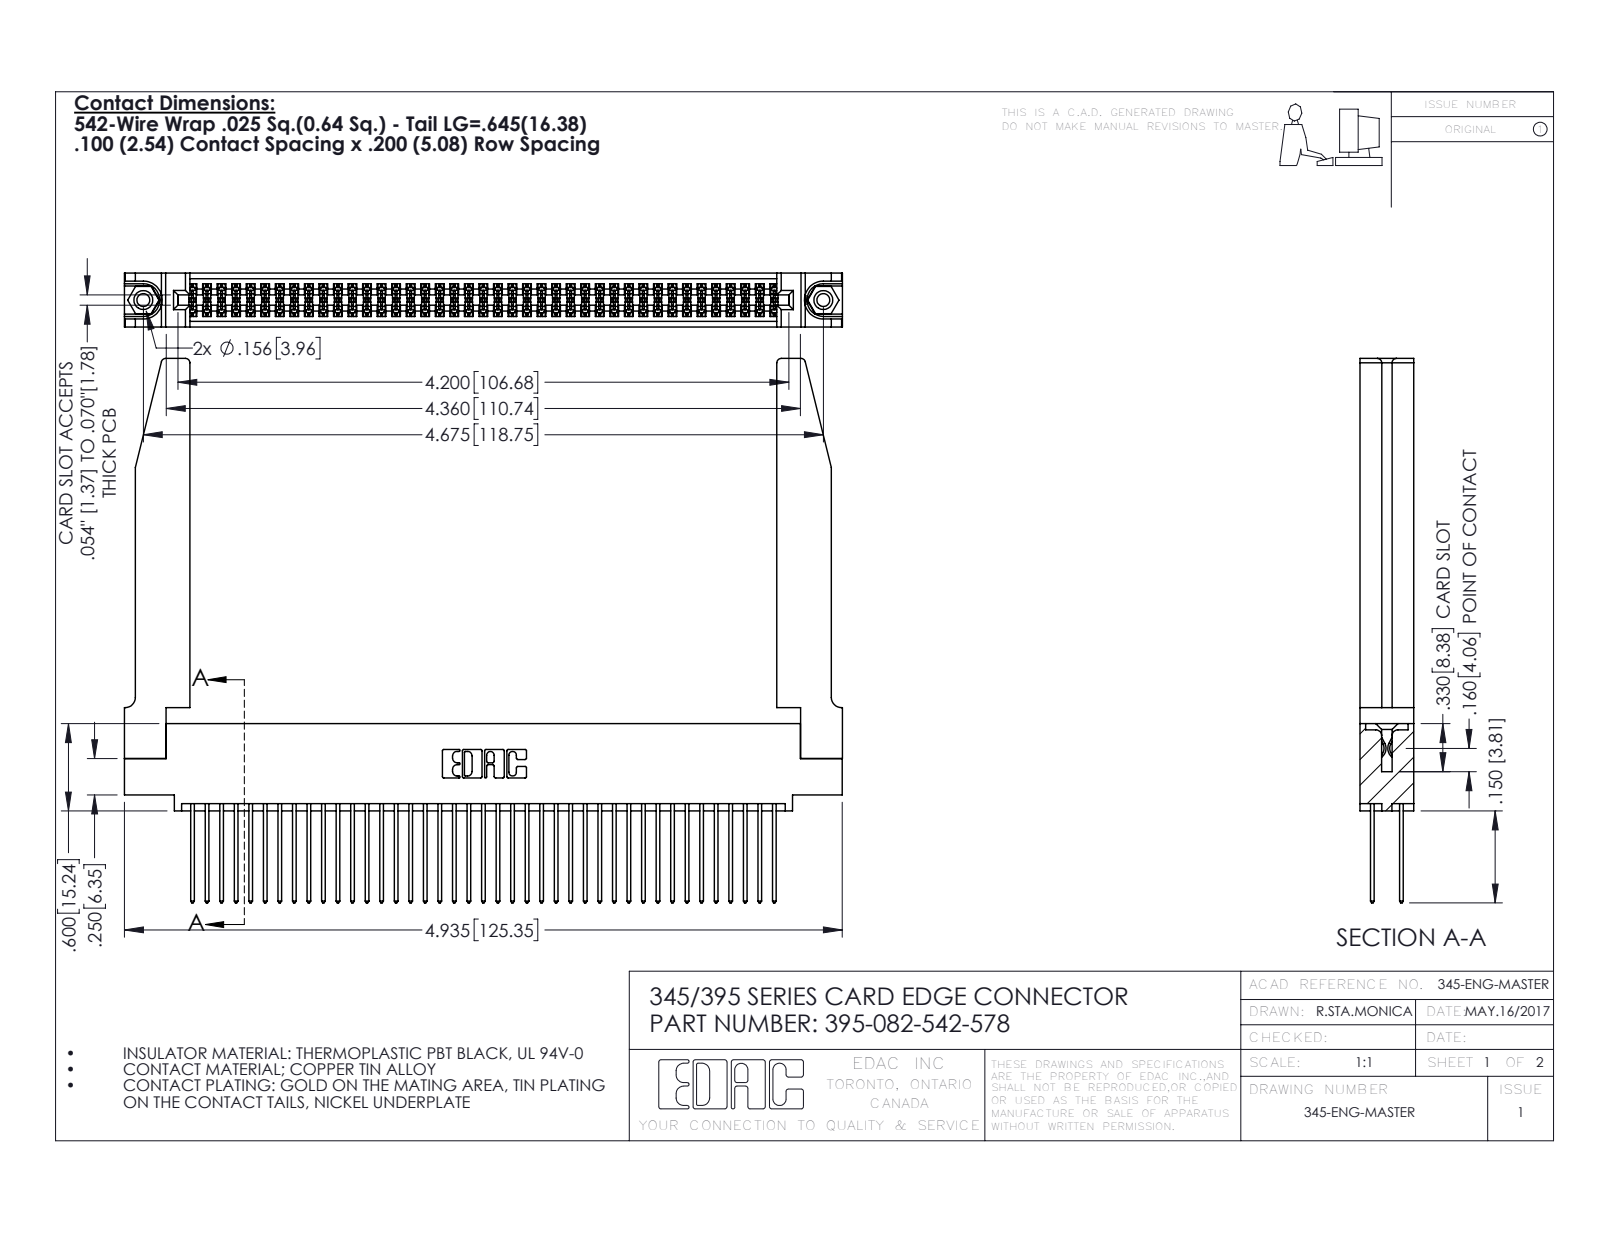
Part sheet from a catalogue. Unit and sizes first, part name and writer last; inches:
Units: inches
Overall size (bounding box): 4.936 × 3.742 × 0.37
Round holes (diameter × count): ⌀0.089 ×2, ⌀0.125 ×2, ⌀0.156 ×2, ⌀0.064 ×1
Round bosses / shafts (diameter × count): ⌀0.155 ×2
Partial cylindrical surfaces — rounded edges, fillets, slot ends (radius × count): R0.006 ×123, R0.01 ×82, R0.01 ×22, R0.03 ×8, R0.007 ×6, R0.031 ×6, R0.026 ×3, R0.014 ×2
Main face-to-face distances: 0.072, 0.298, 0.37, 0.2, 0.098, 0.272, 0.025, 0.225, 0.175, 0.148
Hole centre spacings: 0.27, 4.439, 4.675
Volume: 1.236 in³ · Surface area: 42.07 in²
Bodies: 87 solids, 4464 faces (2932 planar, 1480 cylindrical, 52 other)
Part name (STEP PRODUCT): 345 Part_0.110 Offset - 0.156 Dia-TH; 345-220-078_345-220-078; 345-292-001_345-293-142; 395-082-542-578 (+1 more)
STEP written by: SolidWorks 2016 (CONFIG_CONTROL_DESIGN)
